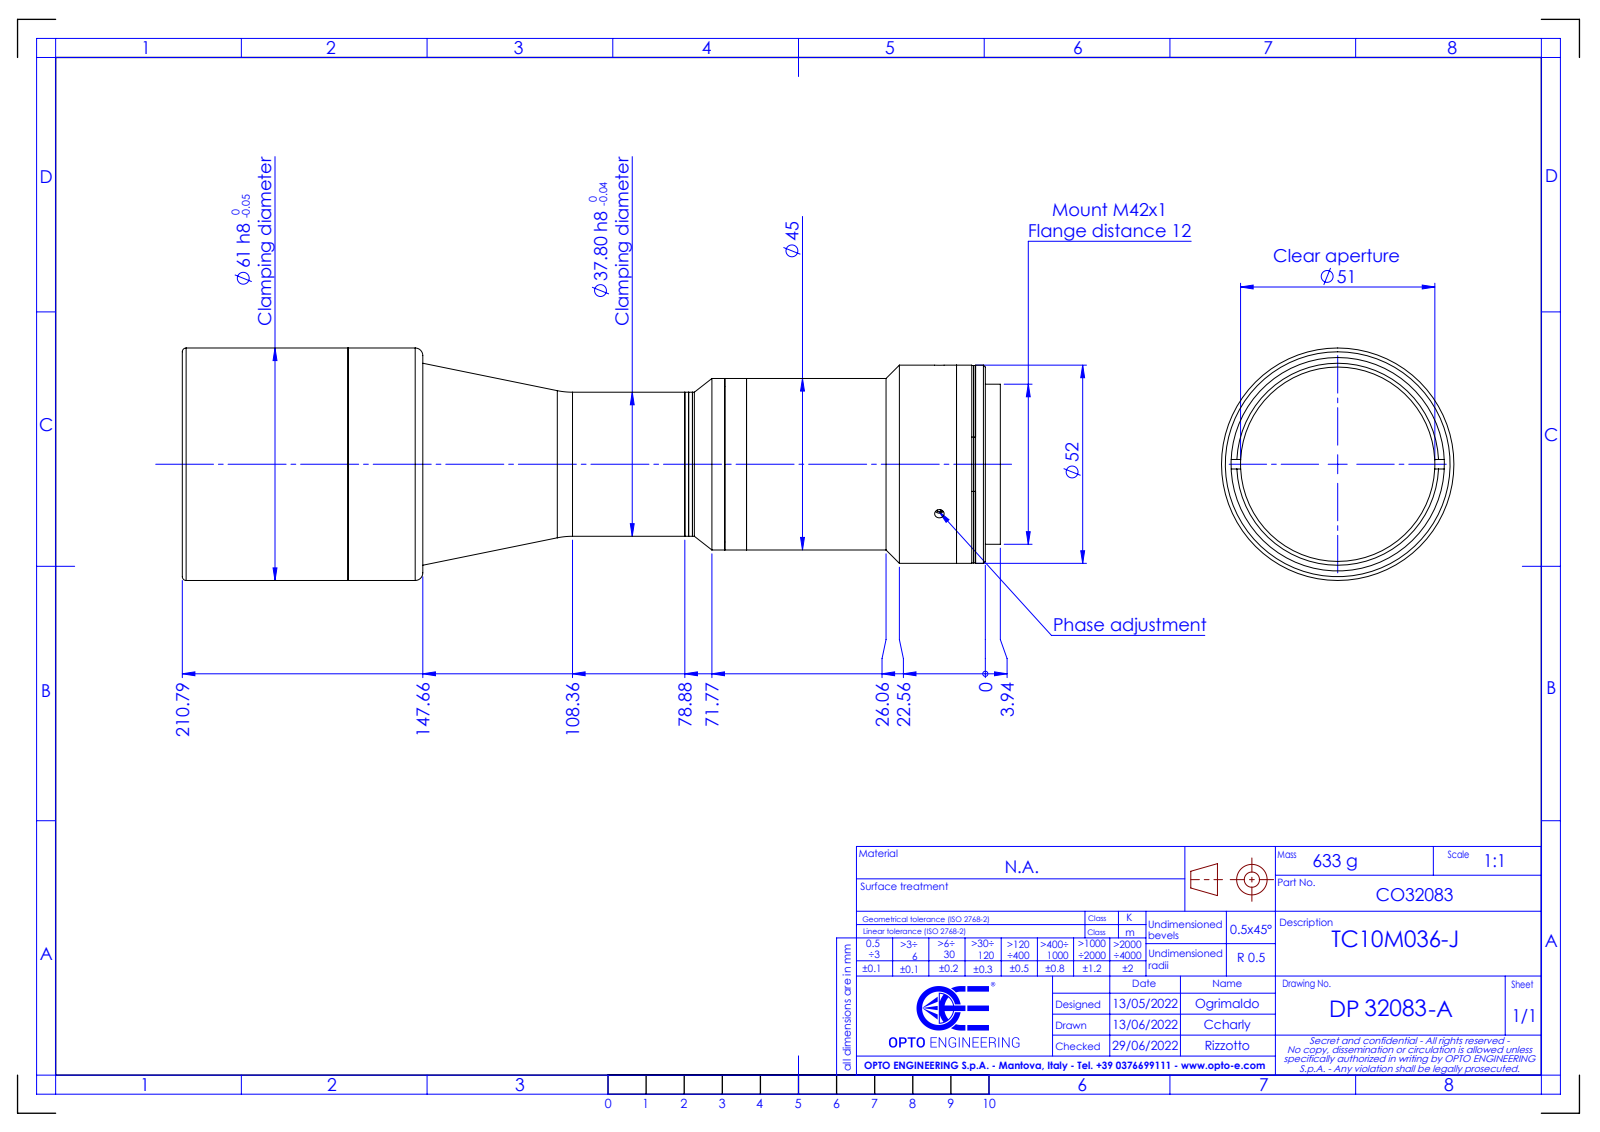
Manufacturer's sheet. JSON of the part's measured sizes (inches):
{"part_name": "DP32083-A_TC10M036-J", "step_written_by": "SolidWorks 2021 (CONFIG_CONTROL_DESIGN)", "units": "inches", "bodies": {"solids": 0, "faces": 96, "planar": 28, "cylindrical": 46, "other": 22}, "overall_size": [8.454, 2.402, 2.402], "round_holes": [[0.098, 3], [1.496, 1], [1.614, 1], [2.008, 1], [2.205, 1]], "round_bosses_or_shafts": [[2.402, 1], [2.087, 1], [2.047, 1], [2.039, 1], [1.772, 1], [1.654, 1], [1.488, 1]], "face_to_face_distances": [2.926, 0.039, 2.887, 3.027, 0.14, 0.101, 3.559, 6.446, 6.485, 6.586]}
